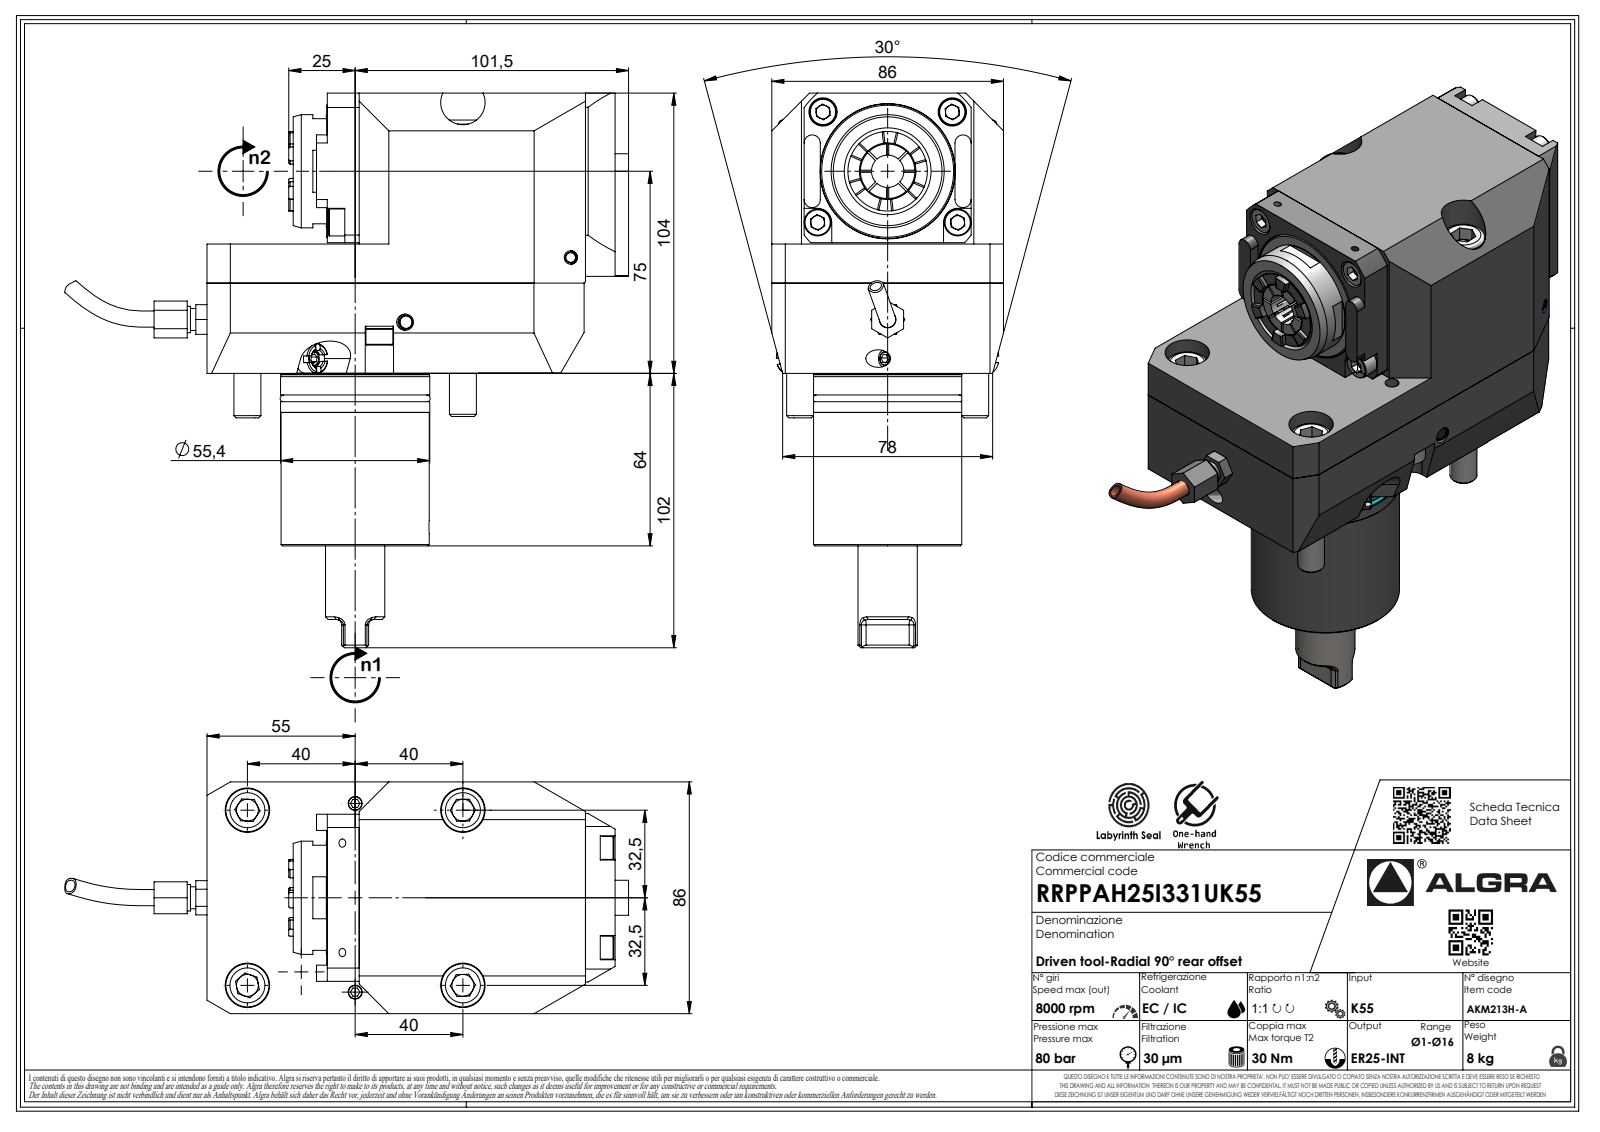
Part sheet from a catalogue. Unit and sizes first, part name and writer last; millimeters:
Units: millimetres
Overall size (bounding box): 209.31 × 205.8 × 86
Round holes (diameter × count): ⌀2.1 ×1, ⌀5 ×1, ⌀6 ×1
Round bosses / shafts (diameter × count): ⌀10 ×4, ⌀55.39 ×1, ⌀55 ×1, ⌀54.99 ×1, ⌀52.81 ×1, ⌀42 ×1, ⌀22 ×1, ⌀9.8 ×1
Partial cylindrical surfaces — rounded edges, fillets, slot ends (radius × count): R0.33 ×7, R0.52 ×7, R3.7 ×7, R2 ×6, R3 ×4, R5.25 ×2, R8 ×2, R8.25 ×2
Main face-to-face distances: 86, 56, 48, 104, 47.8, 103.8, 151.5, 112, 64, 64.2
Volume: 1 202 000 mm³ · Surface area: 85 183 mm²
Bodies: 1 solid, 557 faces (367 planar, 73 cylindrical, 117 other)
Part name (STEP PRODUCT): RRPPAH25I331UK55
STEP written by: SolidWorks 2023 (AUTOMOTIVE_DESIGN)
